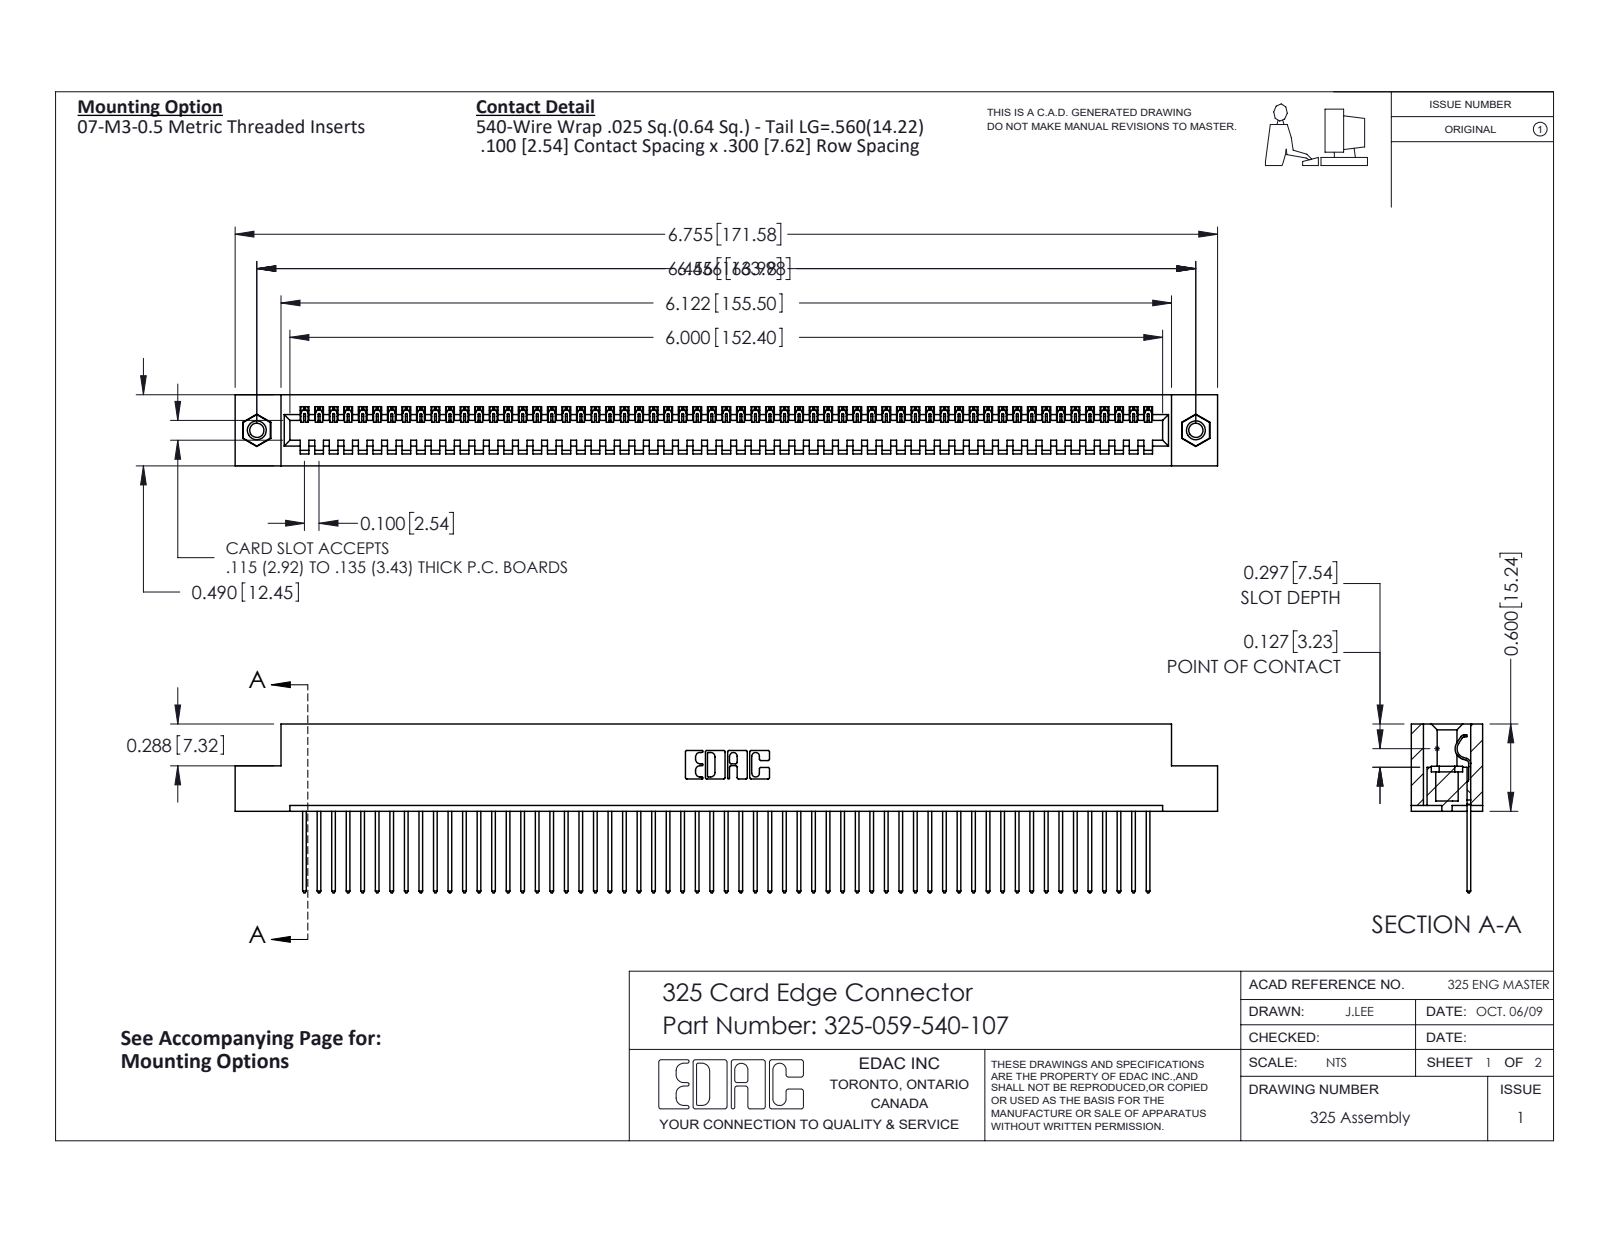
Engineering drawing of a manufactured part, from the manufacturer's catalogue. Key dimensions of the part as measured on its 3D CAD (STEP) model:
Part name (STEP PRODUCT): 325 Part_TI; 325-292-001_325-293-140; 325-059-540-107; 345-250-001_345-250-005-103
STEP written by: SolidWorks 2016 (CONFIG_CONTROL_DESIGN)
Units: inches
Bodies: 62 solids, 3596 faces (2580 planar, 1000 cylindrical, 16 other)
Overall size (bounding box): 6.755 × 1.16 × 0.49
Volume: 1.341 in³ · Surface area: 38.63 in²
Round holes (diameter × count): ⌀0.098 ×2, ⌀0.125 ×2, ⌀0.16 ×2
Round bosses / shafts (diameter × count): ⌀0.155 ×2
Partial cylindrical surfaces — rounded edges, fillets, slot ends (radius × count): R0.006 ×118, R0.01 ×118, R0.01 ×22, R0.007 ×6, R0.031 ×6, R0.026 ×3, R0.014 ×1, R0.022 ×1
Main face-to-face distances: 0.083, 0.407, 0.3, 0.49, 0.107, 0.383, 0.025, 0.325, 0.56, 0.263
Hole centre spacings: 6.456
